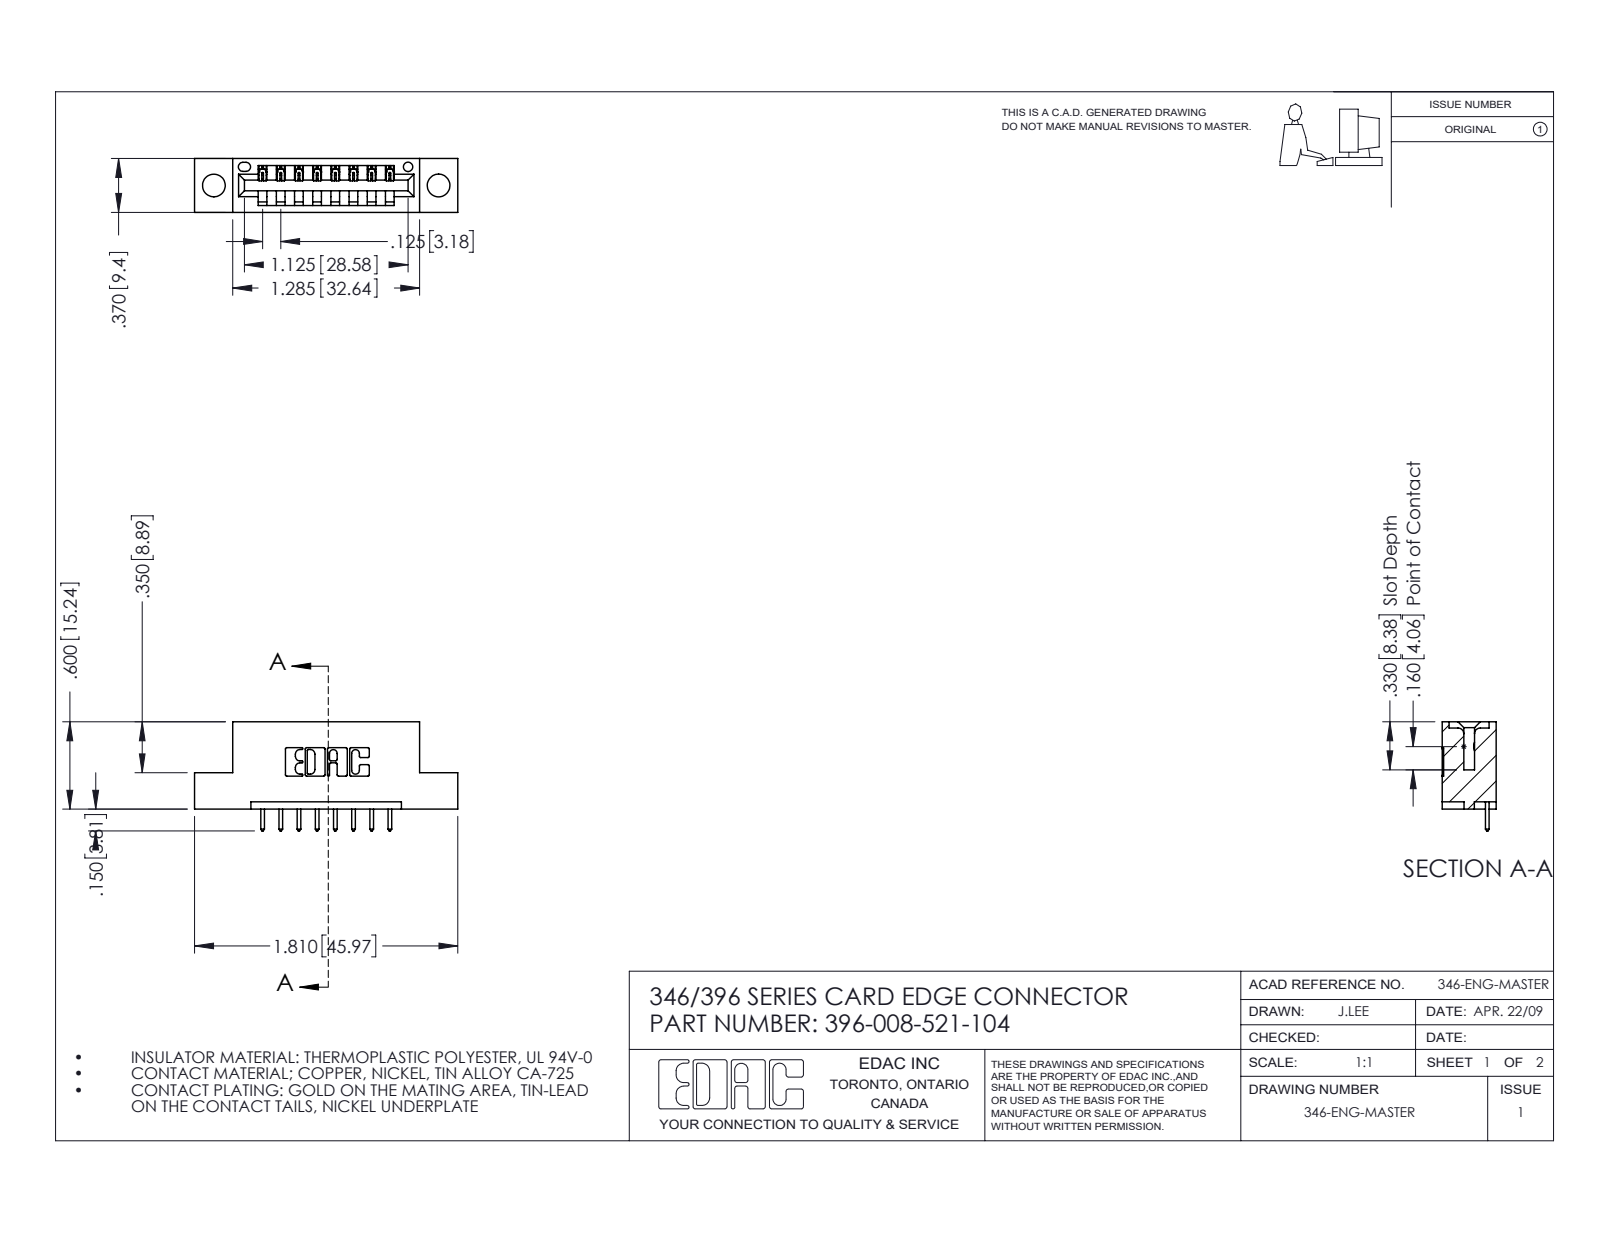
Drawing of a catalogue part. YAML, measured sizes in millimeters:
part_name: "345-292-001_345-293-121; 346 Part_Flush Mounting Lugs - 0.156 Dia-TH; 396-008-521-104"
step_written_by: "SolidWorks 2016 (CONFIG_CONTROL_DESIGN)"
units: millimeters
bodies: {solids: 9, faces: 586, planar: 396, cylindrical: 190, other: 0}
overall_size: [46, 19.1, 9.4]
volume: 4060
surface_area: 4417
round_holes:
  - {diameter: 4, count: 2}
  - {diameter: 1.6, count: 1}
partial_cylinders:
  - {radius: 0.3, count: 22}
  - {radius: 0.2, count: 16}
  - {radius: 0.3, count: 16}
  - {radius: 0.2, count: 6}
  - {radius: 0.8, count: 6}
  - {radius: 0.7, count: 3}
  - {radius: 0.8, count: 2}
  - {radius: 1, count: 2}
face_to_face_distances: [6.4, 9.4, 1.2, 8.2, 12.7, 3.8, 5.6, 2.5, 4.4, 3.2]
hole_center_spacings: [6.2, 34.1, 39.2]
